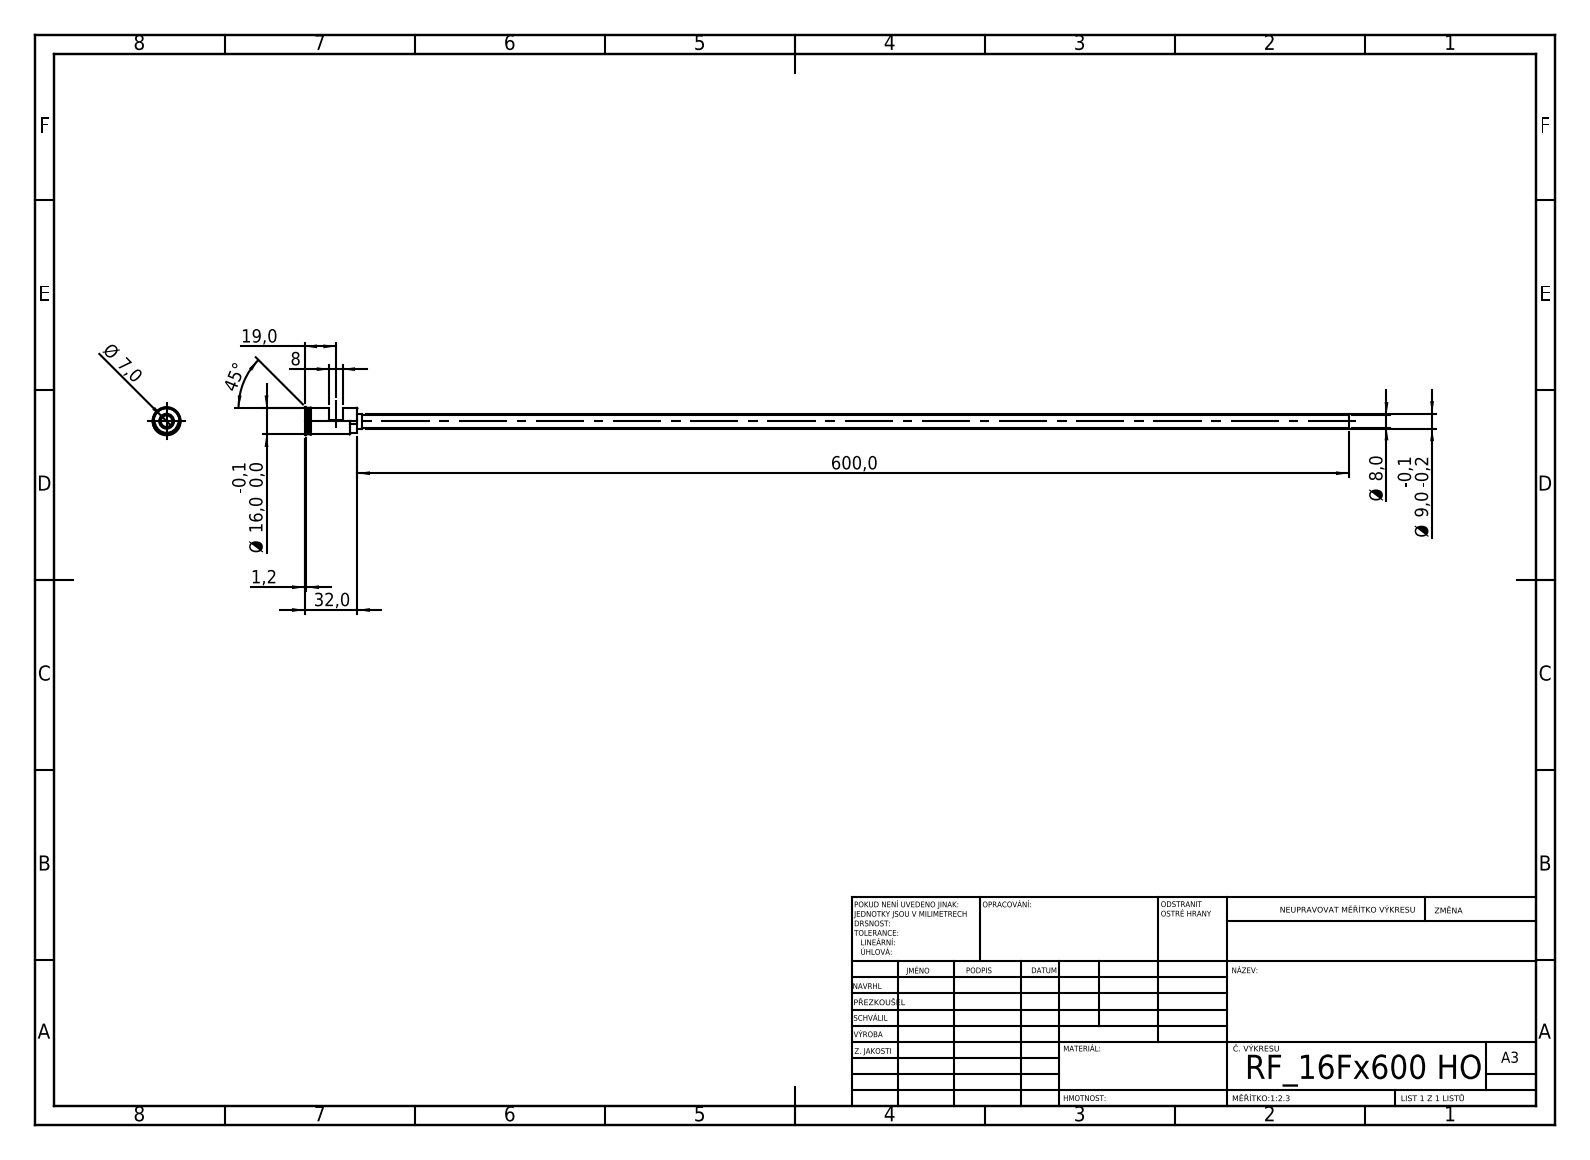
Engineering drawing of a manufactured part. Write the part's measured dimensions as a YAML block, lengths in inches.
step_written_by: "SolidWorks 2019 (CONFIG_CONTROL_DESIGN)"
units: inches
bodies: {solids: 1, faces: 55, planar: 24, cylindrical: 19, other: 12}
overall_size: [24.882, 0.669, 0.669]
volume: 0.73
surface_area: 47.67
round_holes:
  - {diameter: 0.276, count: 1}
round_bosses_or_shafts:
  - {diameter: 0.669, count: 1}
  - {diameter: 0.63, count: 1}
  - {diameter: 0.622, count: 1}
  - {diameter: 0.354, count: 1}
  - {diameter: 0.315, count: 1}
partial_cylinders:
  - {radius: 0.118, count: 2}
  - {radius: 0.278, count: 1}
face_to_face_distances: [0.512, 0.669, 1.181, 0.079, 1.26, 0.591, 0.354, 0.315, 0.827, 0.906]
